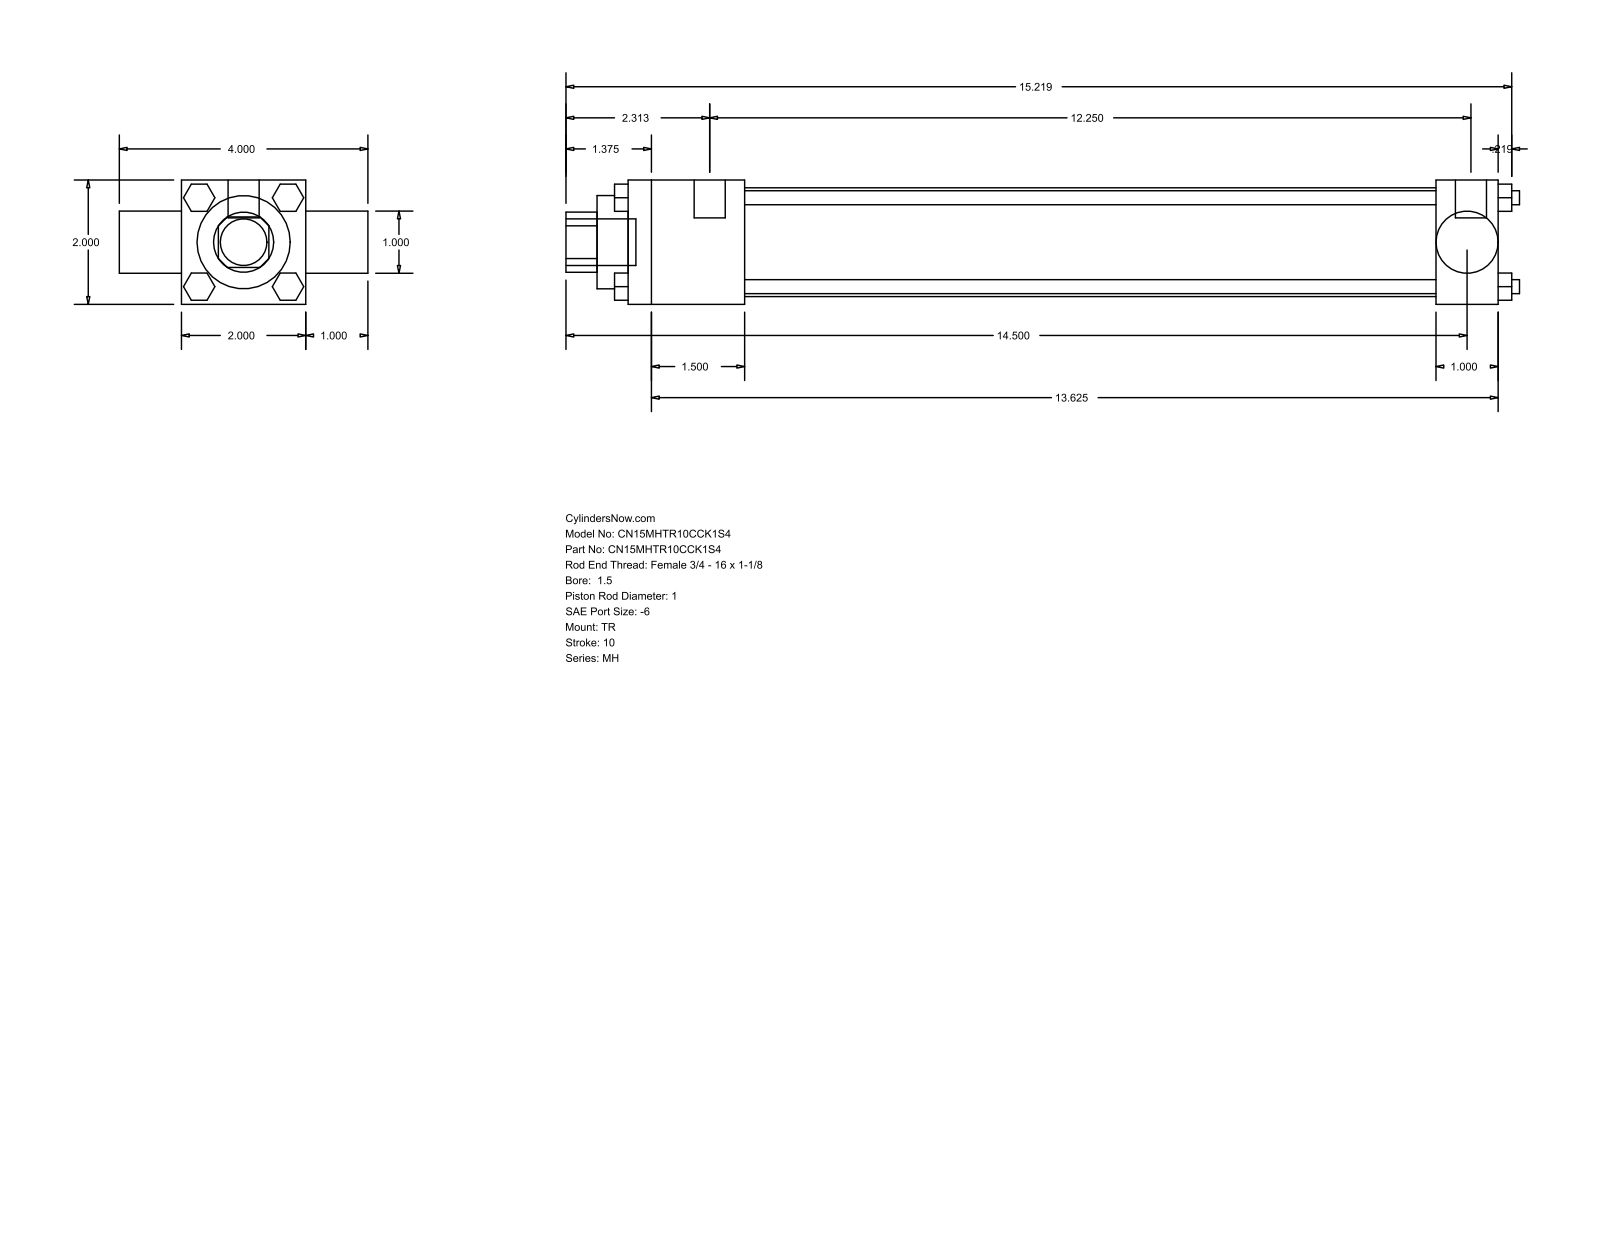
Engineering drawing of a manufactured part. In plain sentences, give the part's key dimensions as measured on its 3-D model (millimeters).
The part is named "MH_TR__0150_1". Its 3-D file was written by "GSSL Pune (CONFIG_CONTROL_DESIGN)". It is 0 solids with 120 faces: 92 planar, 28 cylindrical and 0 other. Overall it measures 389.73 by 101.6 by 50.8 millimeters. Round holes: 1 of diameter 25.35, 1 of diameter 25.4, 1 of diameter 38.1, 1 of diameter 44.45. Round bosses or shafts: 4 of diameter 5.71, 3 of diameter 5.56, 2 of diameter 12.7, 1 of diameter 19.05. Partial cylindrical surfaces (rounded edges, fillets, slot ends): 1 of radius 12.29. The main face-to-face distances are 50.8, 25.4, 355.6, 76.2, 47.63, 307.97, 330.2, 282.57, 361.16, 12.7.
